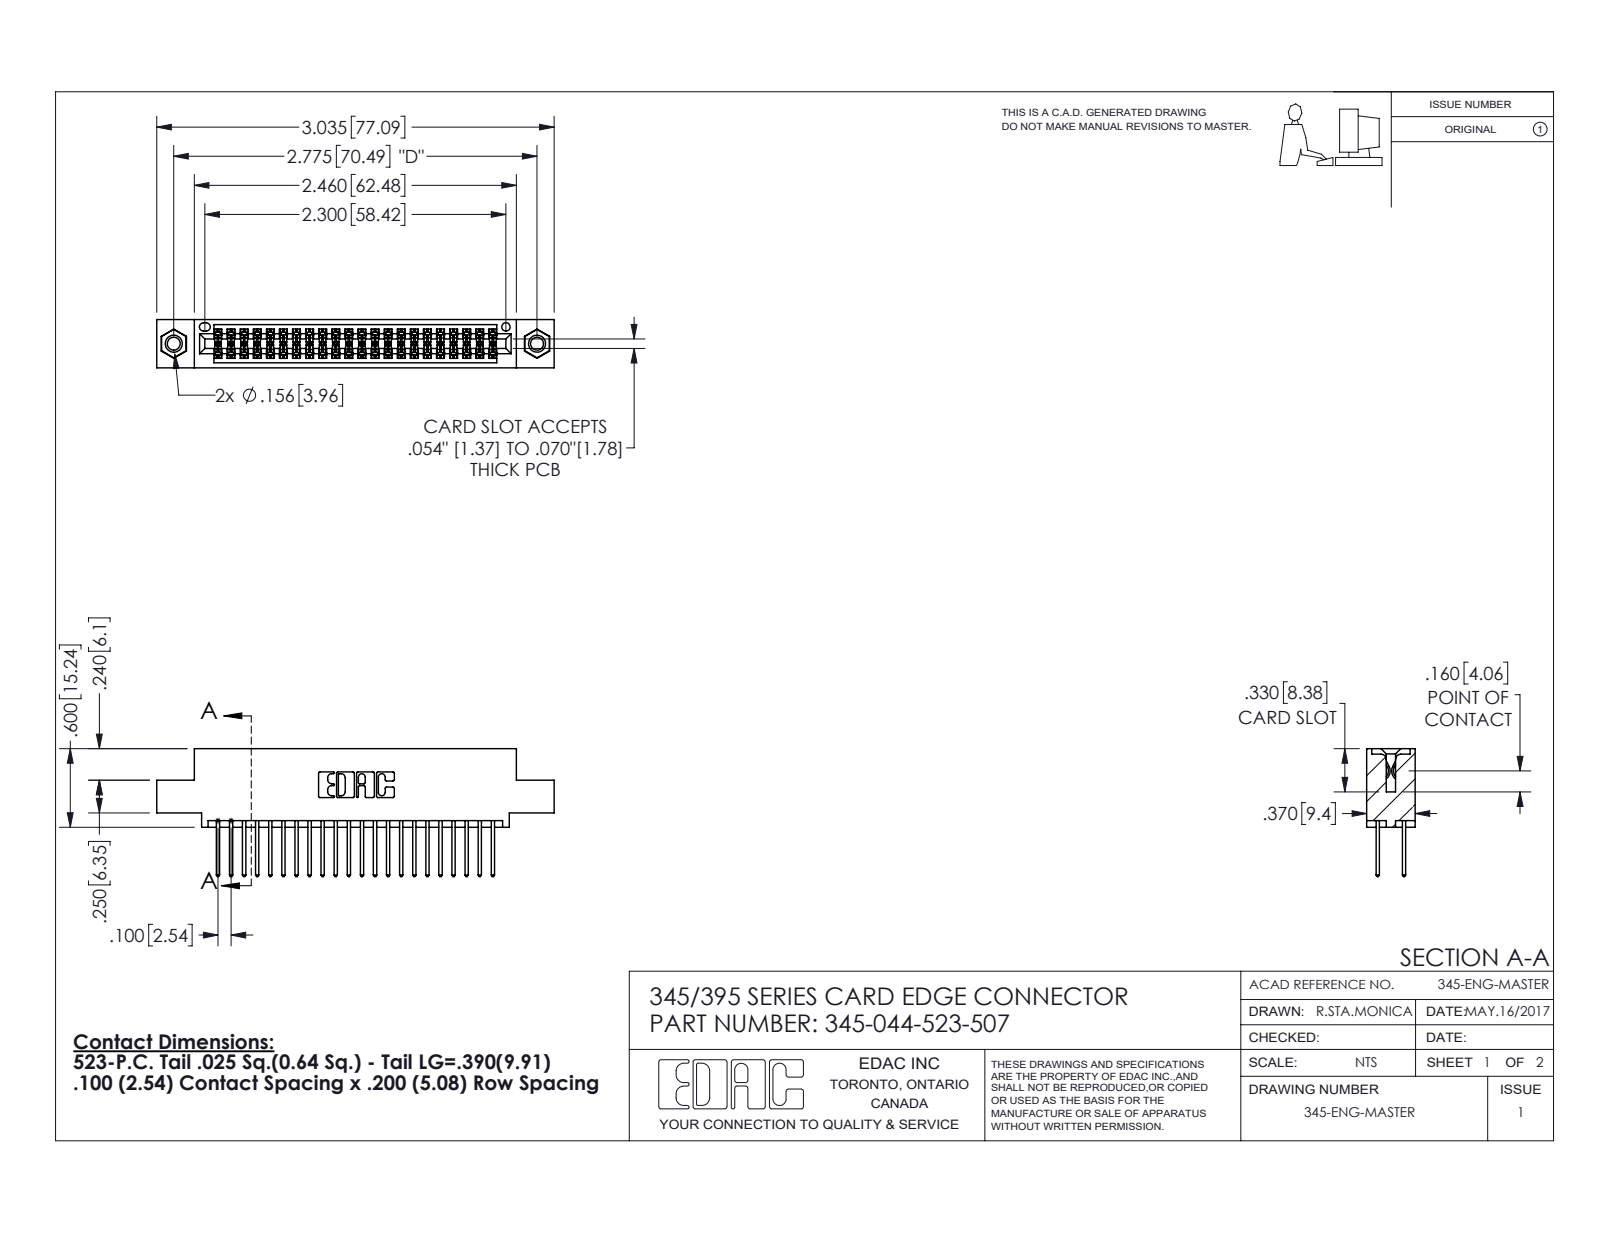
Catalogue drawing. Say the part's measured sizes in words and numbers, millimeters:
The part is named "345-250-001_345-250-005-103; 345-044-523-507; 345-292-001_345-293-123; 345 Part_0.110 Offset - 0.156 Dia-TI". Its 3-D file was written by "SolidWorks 2016 (CONFIG_CONTROL_DESIGN)". It is 47 solids with 2390 faces: 1568 planar, 806 cylindrical and 16 other. Overall it measures 77.1 by 24.8 by 9.4 millimeters. Its volume is 7 310 cubic millimeters and its surface area 10 940 square millimeters. Round holes: 2 of diameter 2.5, 2 of diameter 3.2, 2 of diameter 4, 1 of diameter 1.6. Round bosses or shafts: 2 of diameter 3.9. Partial cylindrical surfaces (rounded edges, fillets, slot ends): 66 of radius 0.2, 44 of radius 0.3, 22 of radius 0.3, 6 of radius 0.2, 6 of radius 0.8, 3 of radius 0.7, 2 of radius 0.4, 2 of radius 0.5. The main face-to-face distances are 1.8, 7.6, 5.1, 2.5, 6.9, 0.6, 9.4, 5.7, 4.4, 3.8. The hole center spacings are 6.9, 64.5, 70.5.
